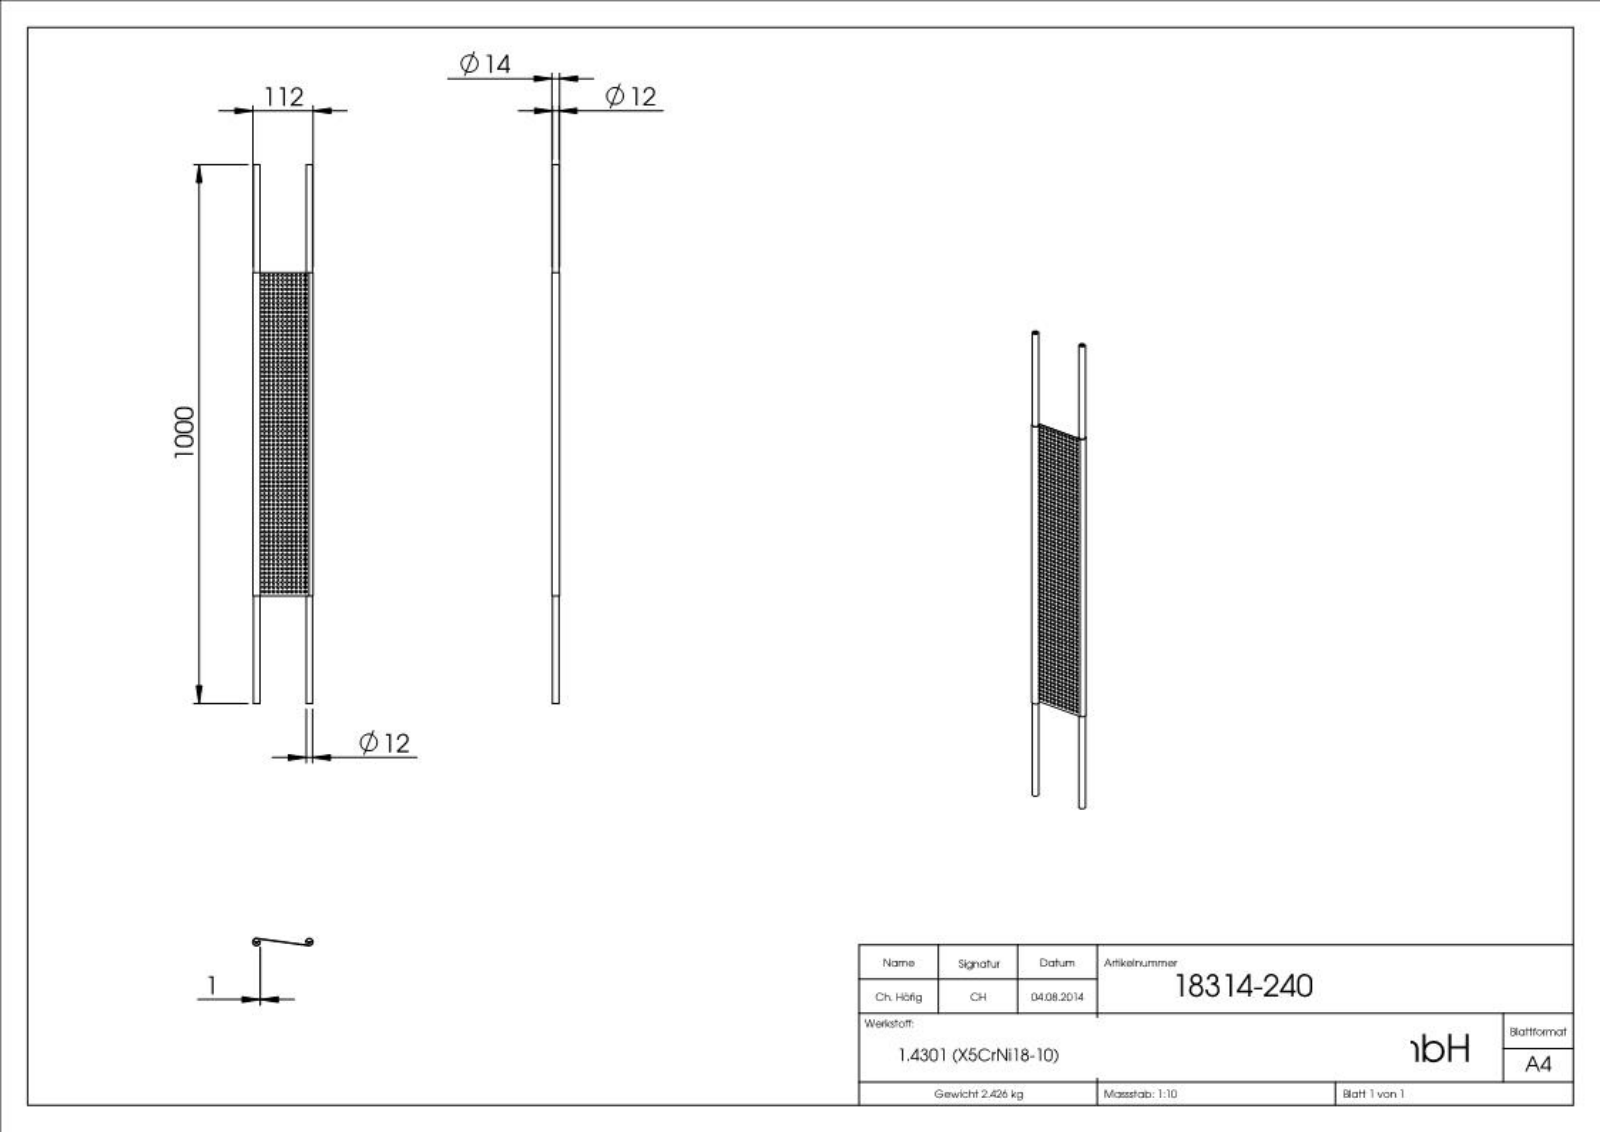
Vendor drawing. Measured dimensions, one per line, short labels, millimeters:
name: 18314-240 Teil2_18314-240 Teil2 Rechts; 18314-240 Teil2_18314-240 Teil2 Links; 18314-240 Teil2; 18314-240 (+2 more)
written by: SolidWorks 2018 (CONFIG_CONTROL_DESIGN)
unit: mm
bodies: 3 solids, 1051 faces (161 planar, 776 cylindrical, 114 other)
size: 1000 × 112 × 14
volume: 307 150 mm³; area: 251 386 mm²
holes: 770× ⌀5, 2× ⌀12
rounds: 2× R7
face distances: 0.97, 200, 800, 1000, 600, 999.9, 799.9, 199.9, 2.23, 1.98
hole spacings: 17, 8.5, 25.5, 34, 42.5, 51, 59.5, 68
